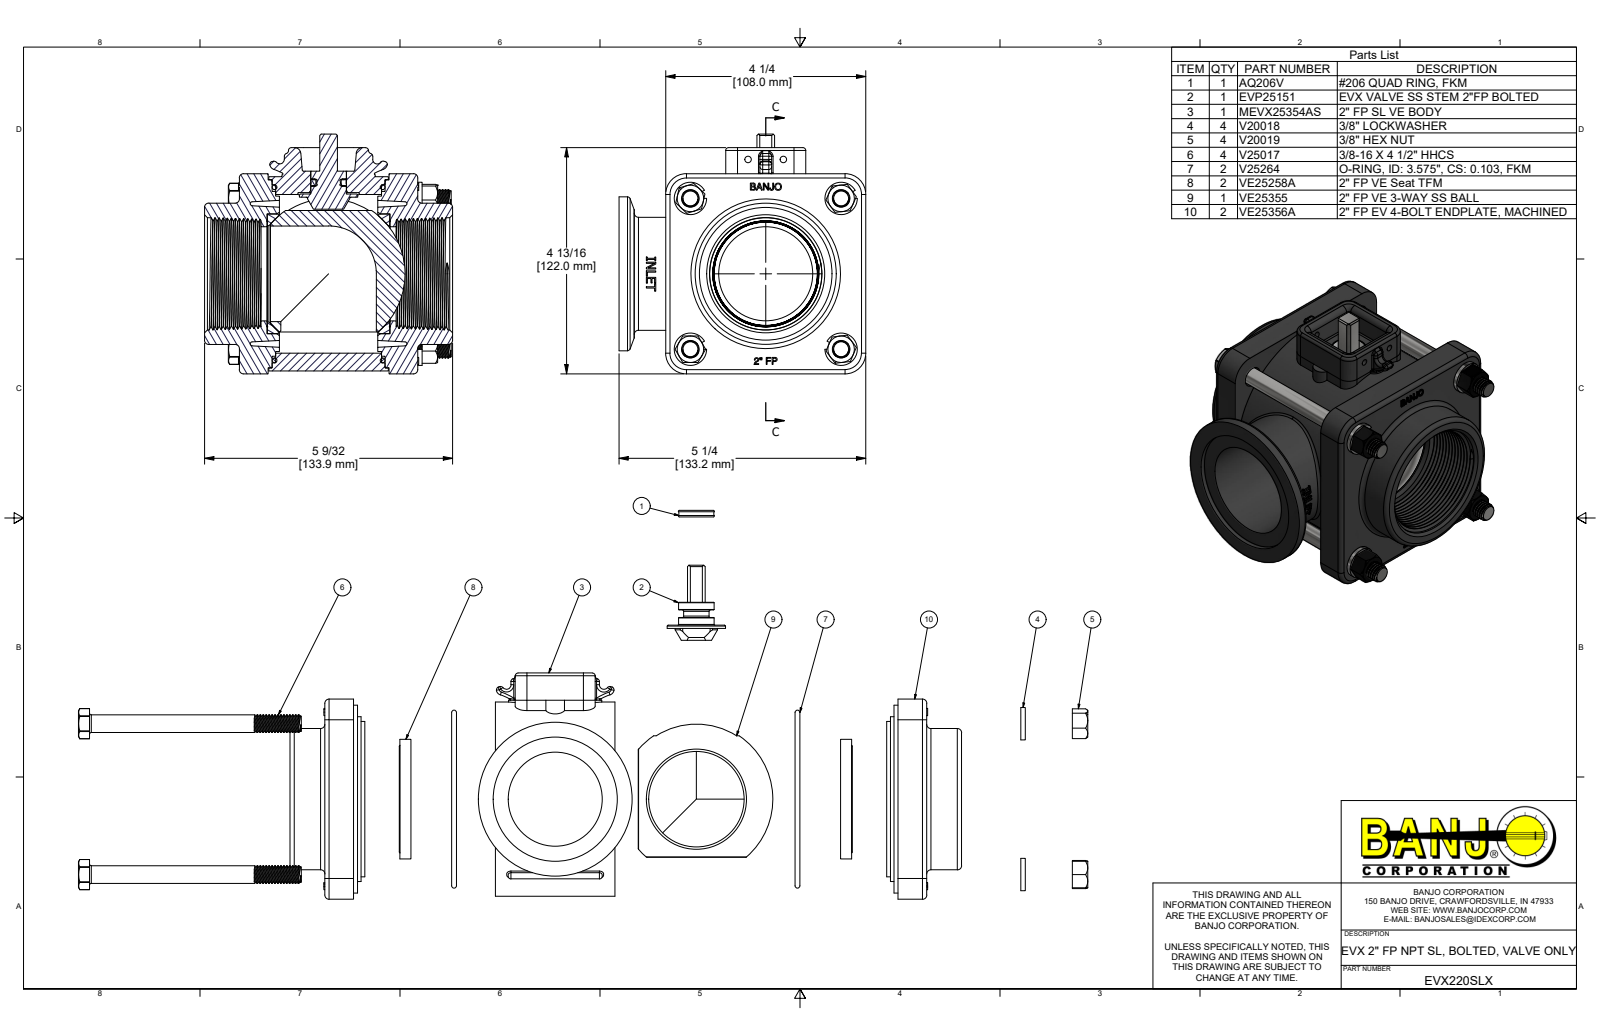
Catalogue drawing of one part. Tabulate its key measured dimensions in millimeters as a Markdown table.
| quantity | value |
| --- | --- |
| part name | EVX220SLX; MEVX25354AS; MEVX25354ASX; V25017 (+8 more) |
| STEP written by | Autodesk Inventor 2019 (AUTOMOTIVE_DESIGN) |
| units | millimeters |
| bodies | 22 solids, 1432 faces (486 planar, 395 cylindrical, 551 other) |
| overall size | 133.9 × 133.2 × 129.4 |
| volume | 736 900 mm³ |
| surface area | 227 500 mm² |
| round holes (diameter × count) | 7.8 × 4, 9.8 × 4, 11.1 × 4, 51.6 × 3, 3.4 × 2, 50.8 × 2, 19.3 × 1, 33 × 1, 51.9 × 1, 64.6 × 1, 66.9 × 1, 85.6 × 1 |
| round bosses / shafts (diameter × count) | 8.2 × 60, 17.4 × 4, 9.5 × 4, 104.8 × 1, 101.3 × 1, 88.9 × 1, 83.8 × 1, 83.1 × 1 |
| partial cylindrical surfaces (radius × count) | 1.5 × 24, 0.8 × 12, 2.3 × 10, 1.6 × 8, 4.1 × 8, 3.2 × 6, 0.5 × 4, 5.3 × 4 |
| main face-to-face distances | 15.5, 80.8, 96.3, 17.7, 78.6, 2.2, 63.1, 108, 4.1, 19.6 |
| hole center spacings | 57.5, 81.4, 37.6, 54.4, 62.4, 107, 114, 115.1 |
